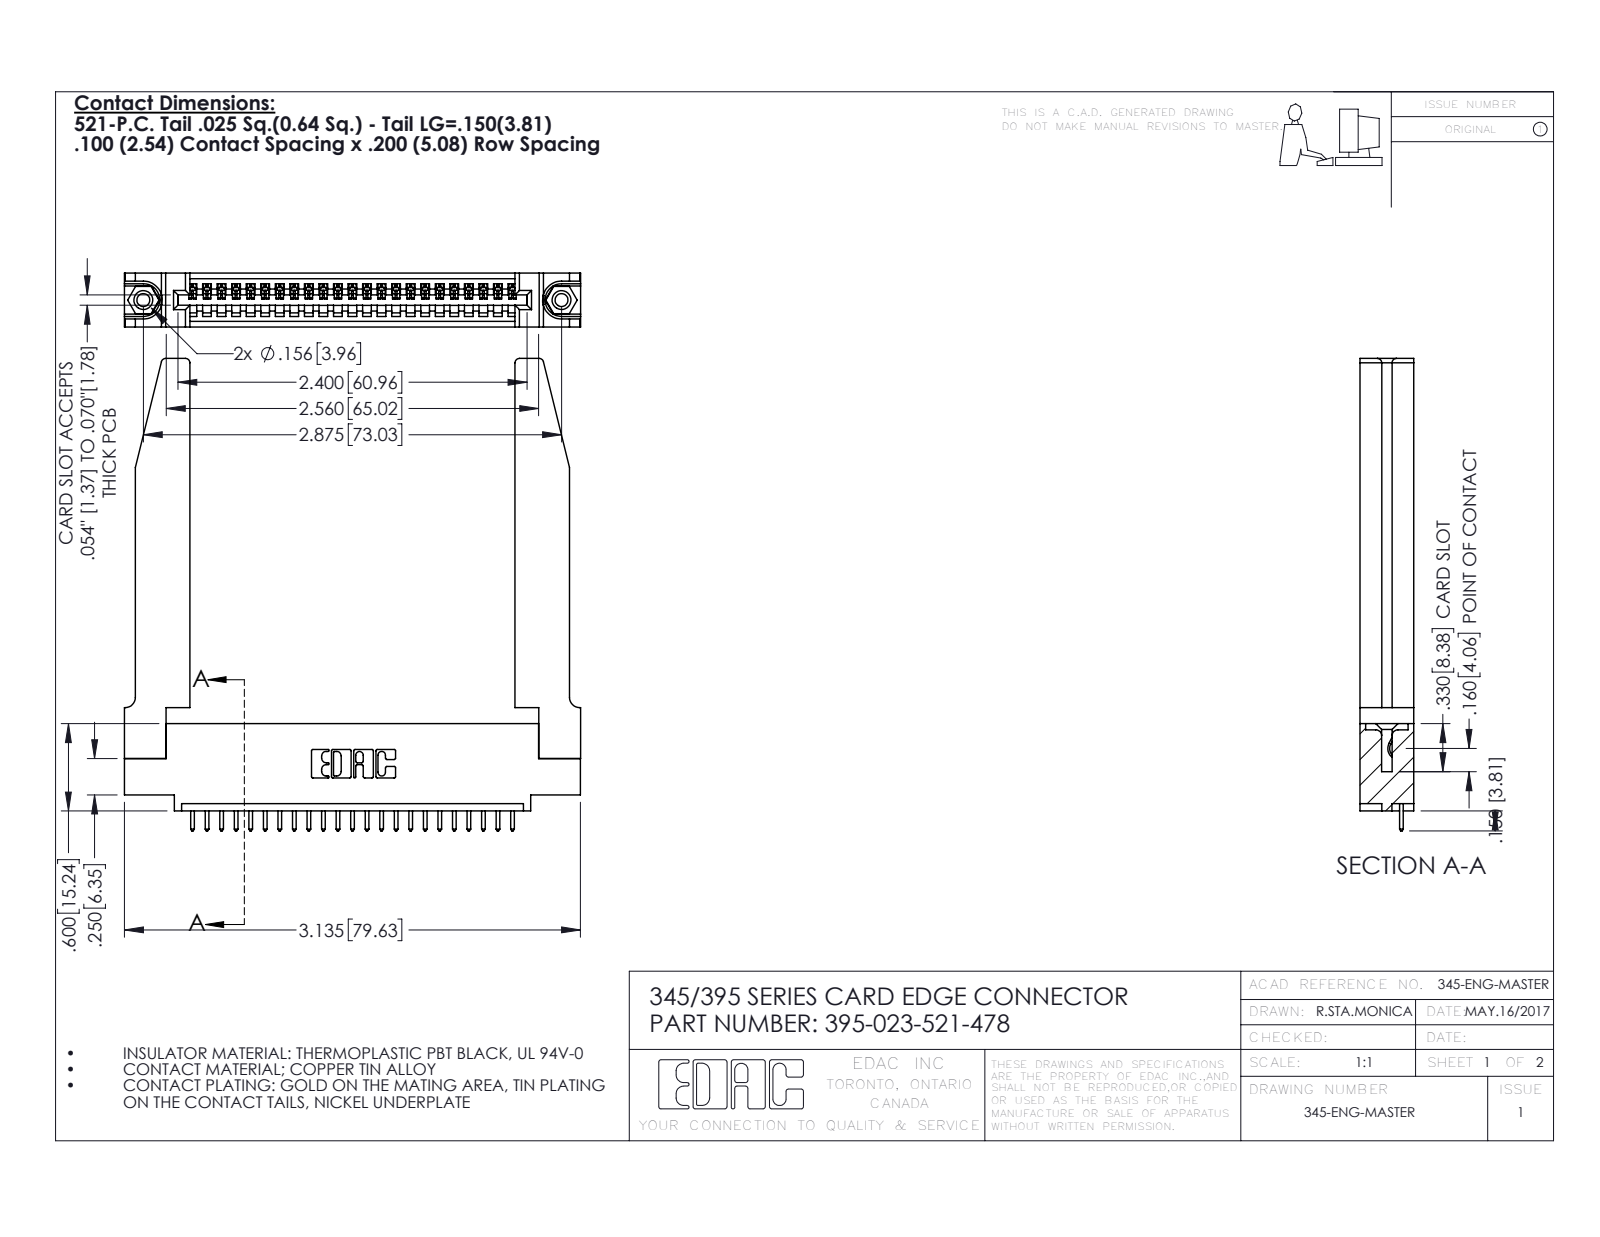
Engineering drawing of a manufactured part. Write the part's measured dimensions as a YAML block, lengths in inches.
part_name: "345-220-078_345-220-078; 345-250-001_345-250-001-102; 345-292-001_345-293-121; 395-023-521-478 (+1 more)"
step_written_by: "SolidWorks 2016 (CONFIG_CONTROL_DESIGN)"
units: inches
bodies: {solids: 28, faces: 1698, planar: 1146, cylindrical: 500, other: 52}
overall_size: [3.247, 3.136, 0.37]
volume: 0.918
surface_area: 24.92
round_holes:
  - {diameter: 0.089, count: 2}
  - {diameter: 0.125, count: 2}
  - {diameter: 0.156, count: 2}
  - {diameter: 0.064, count: 1}
round_bosses_or_shafts:
  - {diameter: 0.155, count: 2}
partial_cylinders:
  - {radius: 0.006, count: 46}
  - {radius: 0.01, count: 46}
  - {radius: 0.01, count: 22}
  - {radius: 0.03, count: 8}
  - {radius: 0.007, count: 6}
  - {radius: 0.031, count: 6}
  - {radius: 0.026, count: 3}
  - {radius: 0.031, count: 2}
face_to_face_distances: [0.37, 0.072, 0.298, 0.2, 0.098, 0.272, 0.025, 0.148, 0.15, 0.22]
hole_center_spacings: [0.27, 2.641, 2.875]
